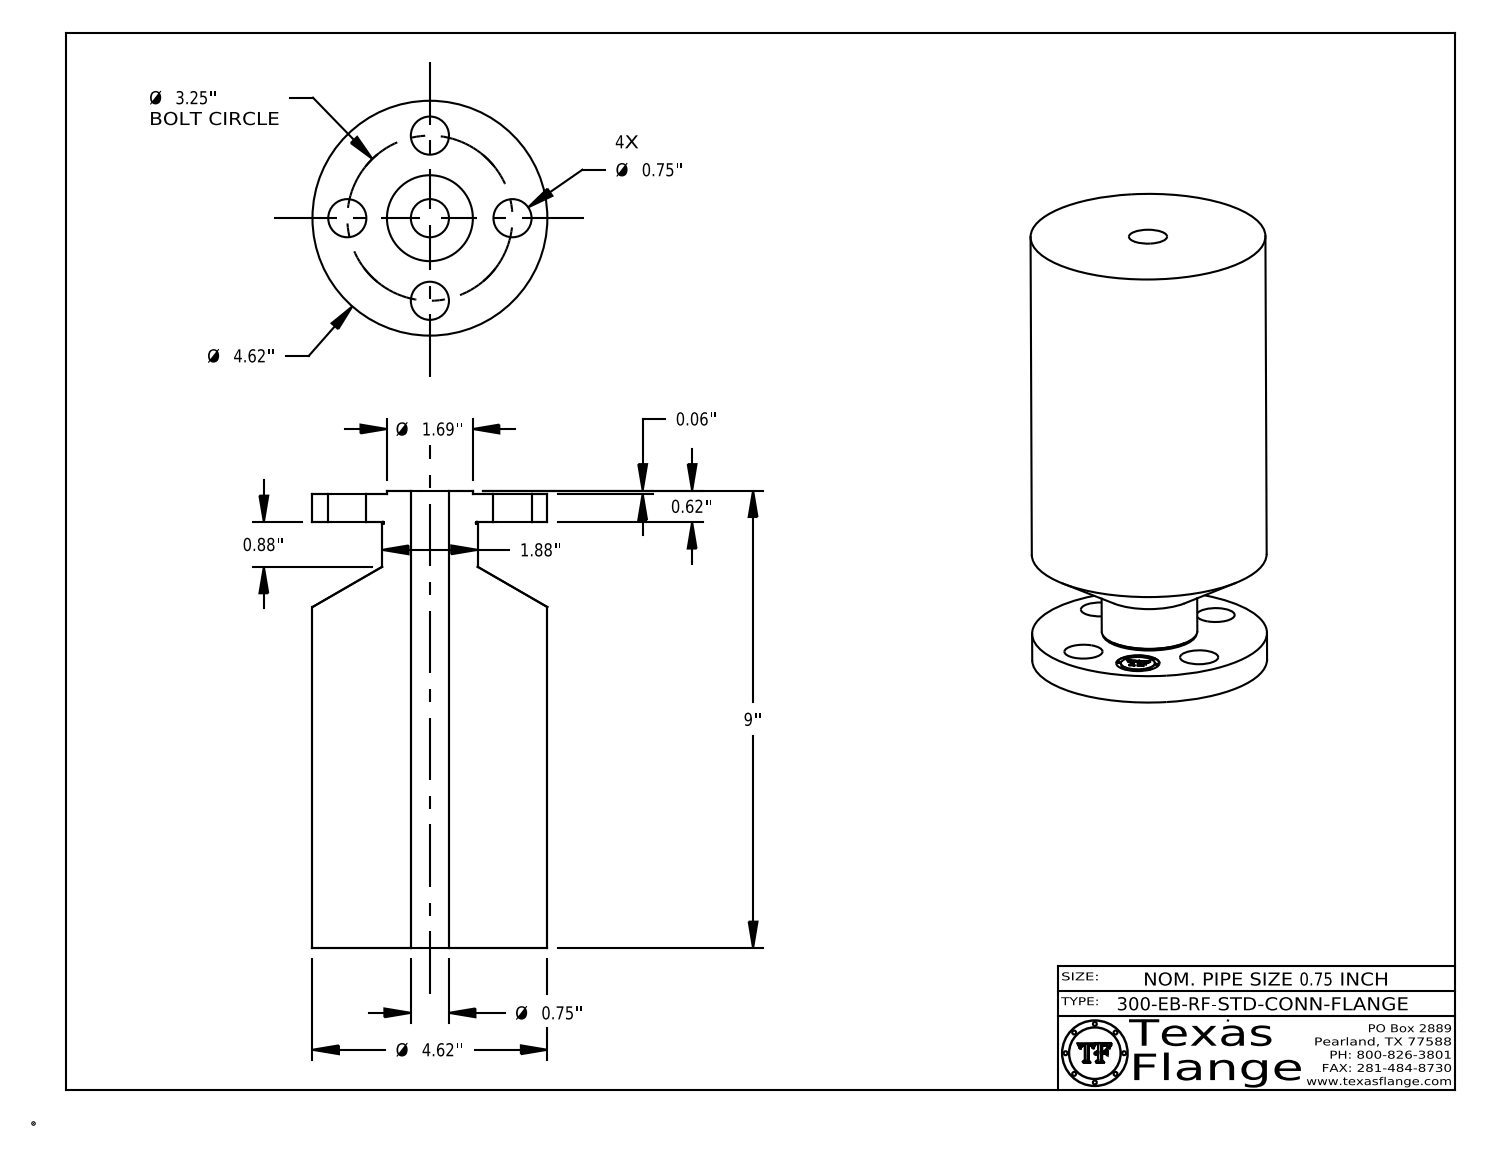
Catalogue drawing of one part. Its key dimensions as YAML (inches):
part_name: "0.75-300-EB-RF-STD-CONN-FLANGE"
step_written_by: "CATIA V5 STEP AP214 (AUTOMOTIVE_DESIGN)"
units: inches
bodies: {solids: 1, faces: 413, planar: 369, cylindrical: 38, other: 6}
overall_size: [9, 4.62, 4.62]
volume: 126.4
surface_area: 197
round_holes:
  - {diameter: 0.75, count: 5}
  - {diameter: 0.85, count: 1}
round_bosses_or_shafts:
  - {diameter: 0.051, count: 8}
  - {diameter: 4.62, count: 1}
  - {diameter: 1.88, count: 1}
  - {diameter: 1.69, count: 1}
  - {diameter: 0.67, count: 1}
face_to_face_distances: [8.937, 0.557, 8.38, 0.063, 0.62, 9, 0.615, 0.552, 8.385, 0.254]
hole_center_spacings: [1.625, 2.298, 1.244, 3.003, 3.25]
